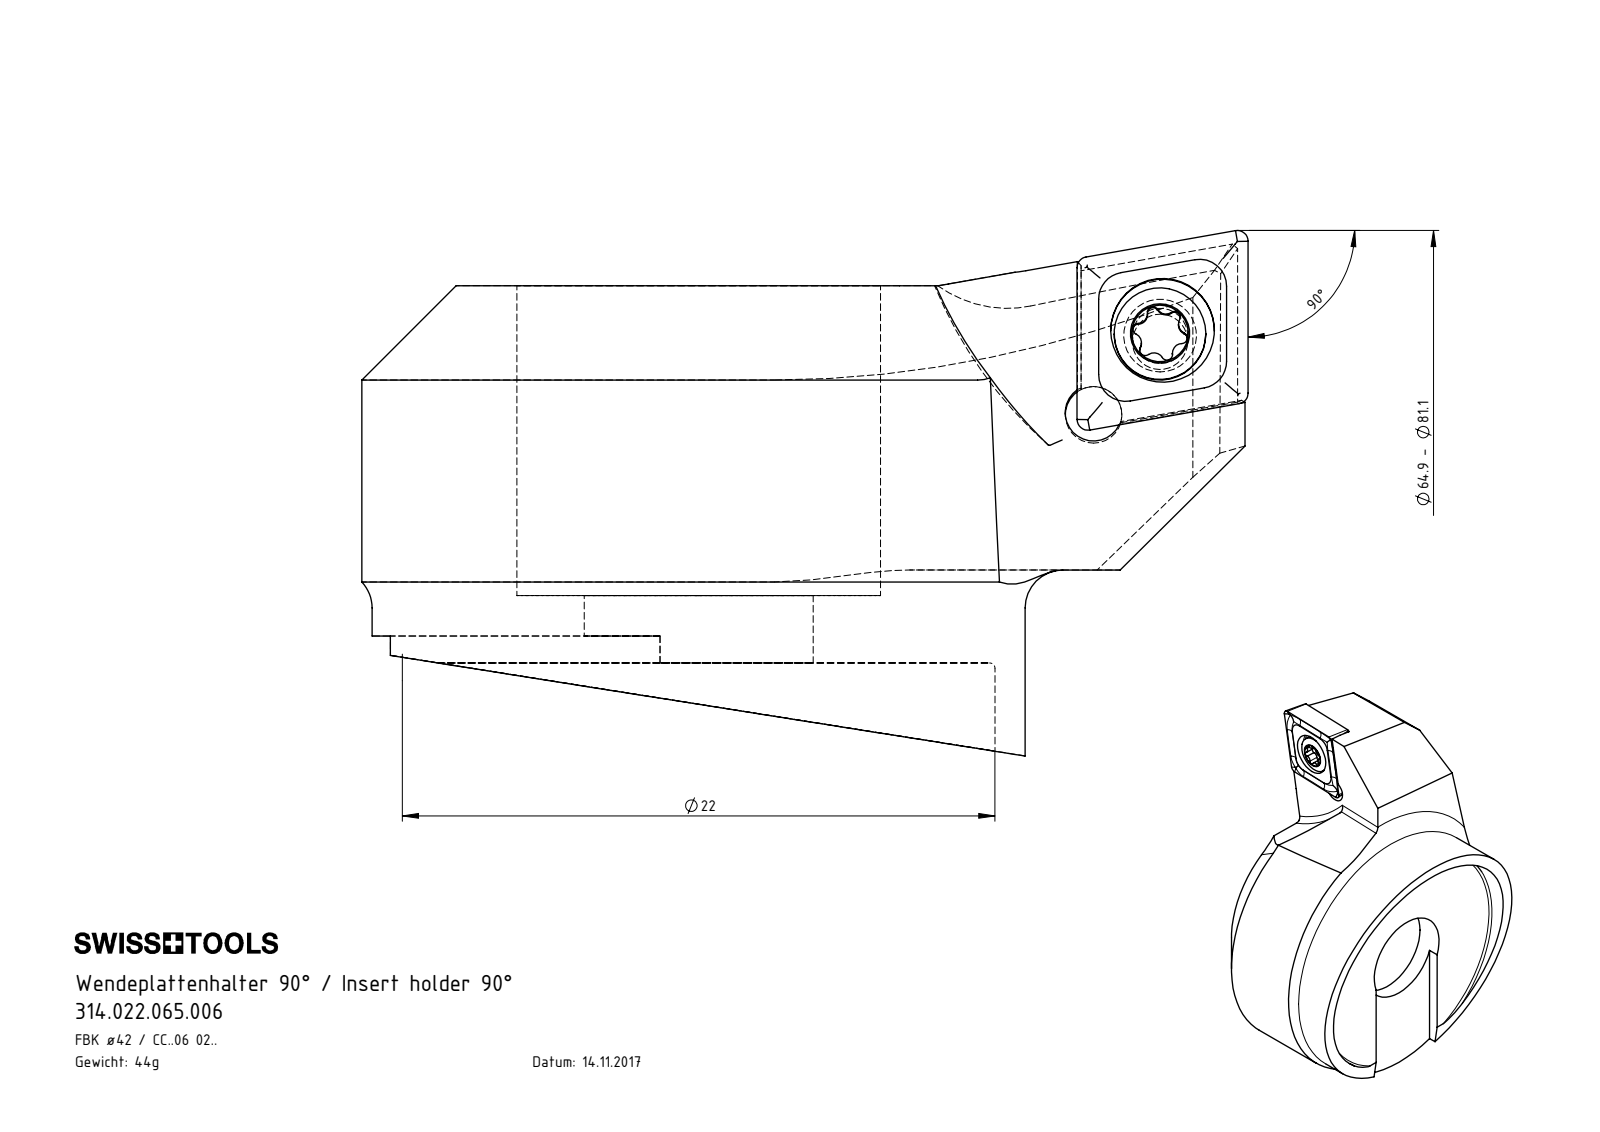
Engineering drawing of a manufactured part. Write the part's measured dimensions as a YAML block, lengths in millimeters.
part_name: "F42-WCA.001.016_A_fertigbearbeitet; CCMT060204; WCA-ER2.001.006_A; F42.WCA.001.016"
step_written_by: "SolidWorks 2017 (AUTOMOTIVE_DESIGN)"
units: millimeters
bodies: {solids: 3, faces: 105, planar: 39, cylindrical: 27, other: 39}
overall_size: [32.9, 25, 19.5]
volume: 5498
surface_area: 3122
round_holes:
  - {diameter: 2.05, count: 1}
  - {diameter: 2.1, count: 1}
  - {diameter: 2.8, count: 1}
  - {diameter: 3.85, count: 1}
  - {diameter: 8.5, count: 1}
  - {diameter: 13.5, count: 1}
round_bosses_or_shafts:
  - {diameter: 24.25, count: 1}
  - {diameter: 3.4, count: 1}
  - {diameter: 2.5, count: 1}
partial_cylinders:
  - {radius: 0.21, count: 6}
  - {radius: 0.36, count: 5}
  - {radius: 0.5, count: 2}
  - {radius: 0.36, count: 1}
  - {radius: 5, count: 1}
  - {radius: 11, count: 1}
  - {radius: 12.5, count: 1}
  - {radius: 16, count: 1}
face_to_face_distances: [14, 11.5, 2.5, 13, 1.5, 1, 2.28, 10.55, 0.95, 2.45]
hole_center_spacings: [3.84, 4]
